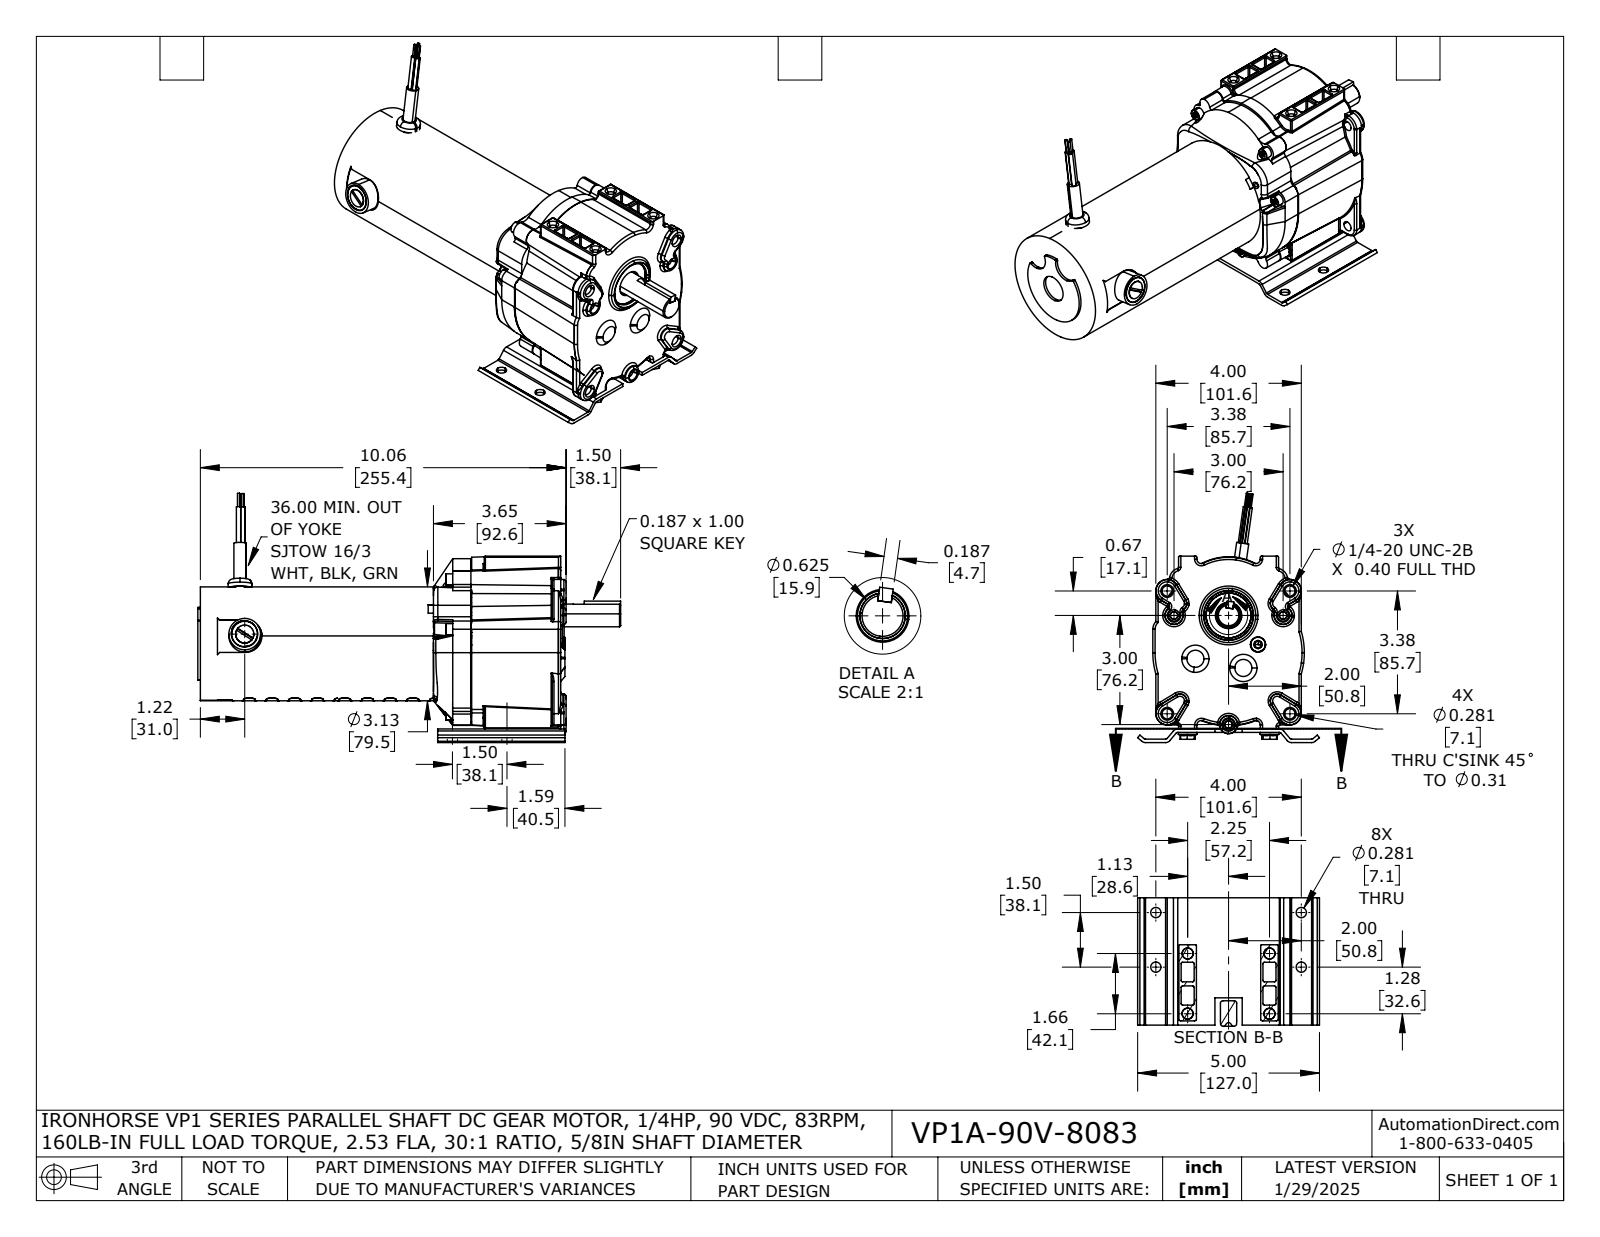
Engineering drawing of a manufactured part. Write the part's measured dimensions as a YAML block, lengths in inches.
part_name: "VP1A-90V-8083"
step_written_by: "SolidWorks 2024 (AUTOMOTIVE_DESIGN)"
units: inches
bodies: {solids: 10, faces: 2472, planar: 654, cylindrical: 701, other: 1117}
overall_size: [11.627, 6.854, 5]
volume: 98.93
surface_area: 345.4
round_holes:
  - {diameter: 0.281, count: 12}
  - {diameter: 0.218, count: 5}
  - {diameter: 0.159, count: 3}
  - {diameter: 0.207, count: 3}
  - {diameter: 0.135, count: 2}
  - {diameter: 0.166, count: 2}
  - {diameter: 0.204, count: 2}
  - {diameter: 0.397, count: 2}
  - {diameter: 0.688, count: 2}
  - {diameter: 0.875, count: 2}
  - {diameter: 0.75, count: 1}
  - {diameter: 0.813, count: 1}
round_bosses_or_shafts:
  - {diameter: 0.307, count: 5}
  - {diameter: 0.19, count: 5}
  - {diameter: 0.51, count: 4}
  - {diameter: 0.3, count: 4}
  - {diameter: 0.12, count: 3}
  - {diameter: 0.06, count: 3}
  - {diameter: 0.873, count: 2}
  - {diameter: 0.733, count: 2}
partial_cylinders:
  - {radius: 0.03, count: 52}
  - {radius: 0.031, count: 38}
  - {radius: 0.062, count: 23}
  - {radius: 0.12, count: 18}
  - {radius: 0.156, count: 18}
  - {radius: 0.19, count: 10}
  - {radius: 0.151, count: 9}
  - {radius: 0.161, count: 9}
face_to_face_distances: [0.095, 2.449, 3.5, 1.051, 9.44, 6.991, 5.94, 0.47, 6.97, 9.91]
hole_center_spacings: [1.5, 3.375, 1.691, 0.492, 0.698, 1.224, 1.426, 1.552]
